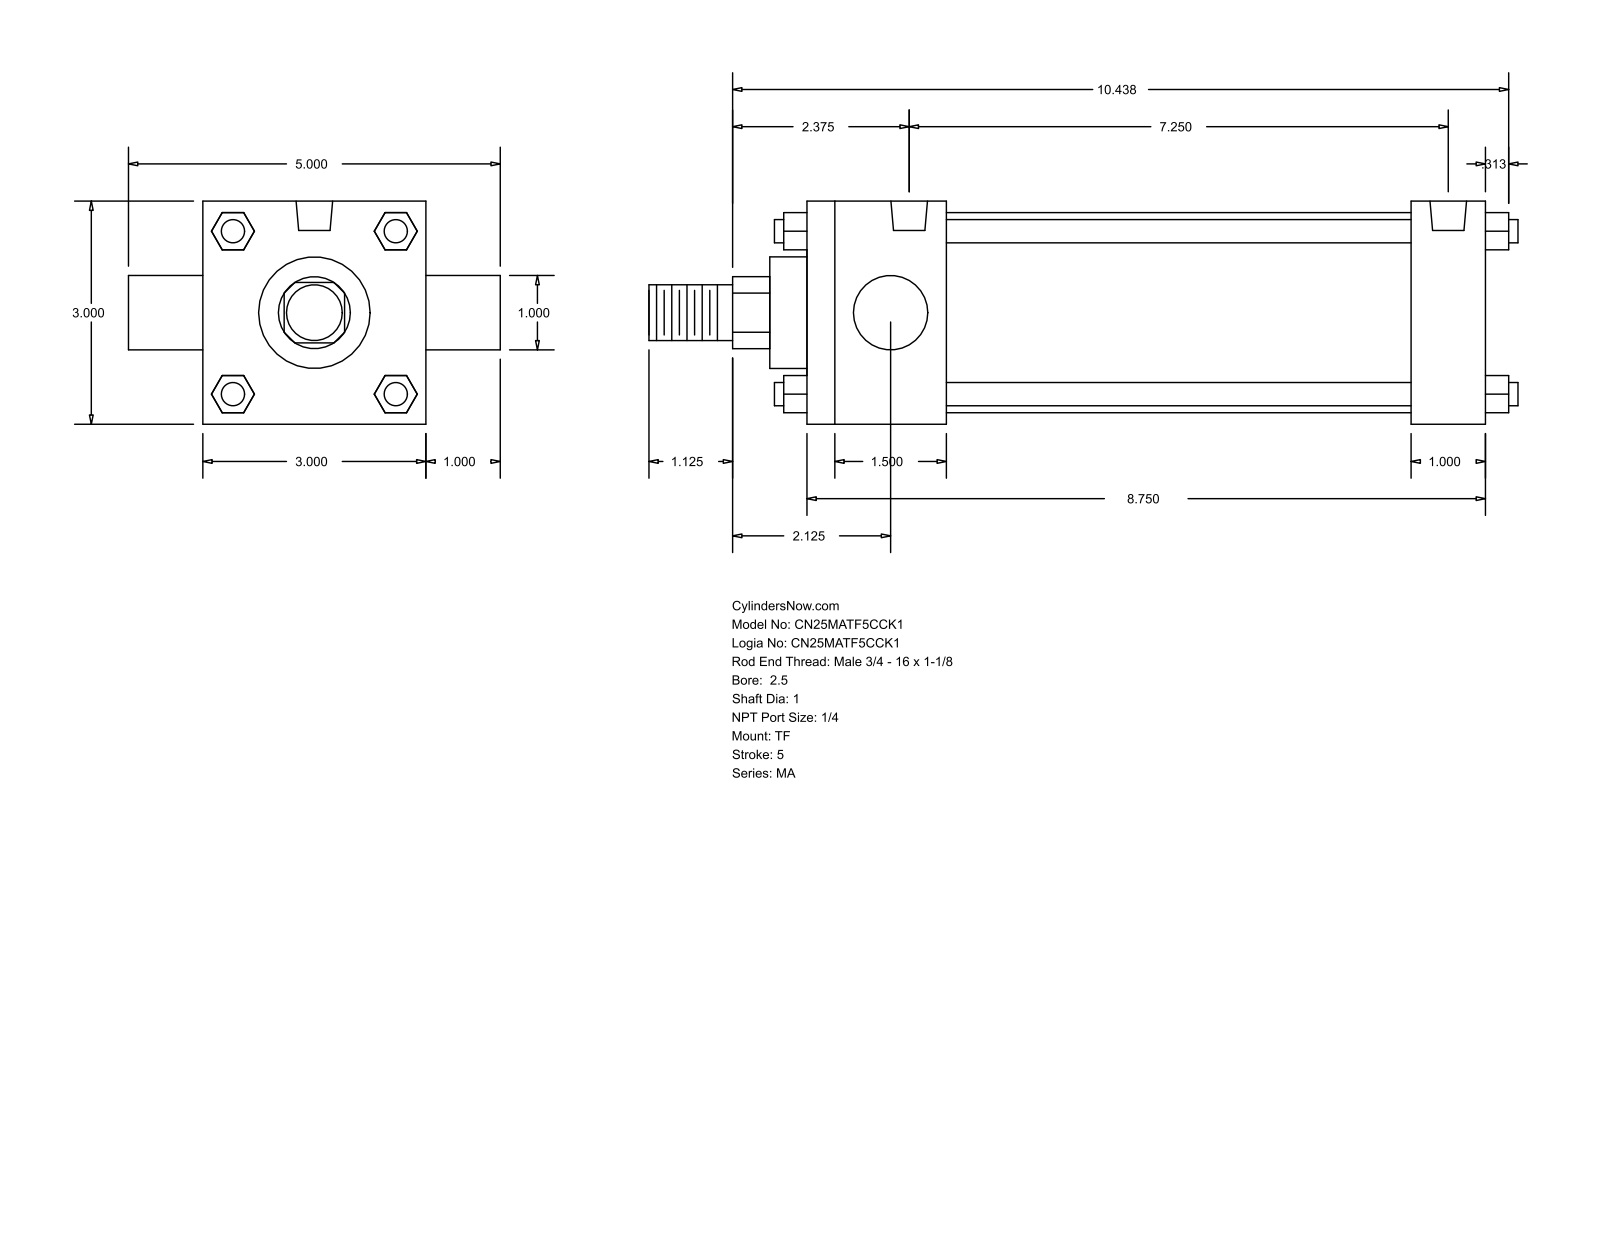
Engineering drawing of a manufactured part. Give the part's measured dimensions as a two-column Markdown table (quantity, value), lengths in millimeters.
| quantity | value |
| --- | --- |
| part name | MA_TF__0250_1 |
| STEP written by | GSSL Pune (CONFIG_CONTROL_DESIGN) |
| units | millimeters |
| bodies | 0 solids, 120 faces (92 planar, 28 cylindrical, 0 other) |
| overall size | 296.86 × 127 × 76.2 |
| round holes (diameter × count) | 7.94 × 3, 12.49 × 2 |
| round bosses / shafts (diameter × count) | 7.94 × 4, 25.4 × 2, 68.33 × 1, 38.1 × 1, 19.05 × 1 |
| partial cylindrical surfaces (radius × count) | 12.29 × 1 |
| main face-to-face distances | 76.2, 231.78, 25.4, 12.7, 47.63, 206.38, 158.75, 184.15, 101.6, 27.81 |
| hole center spacings | 184.14 |
